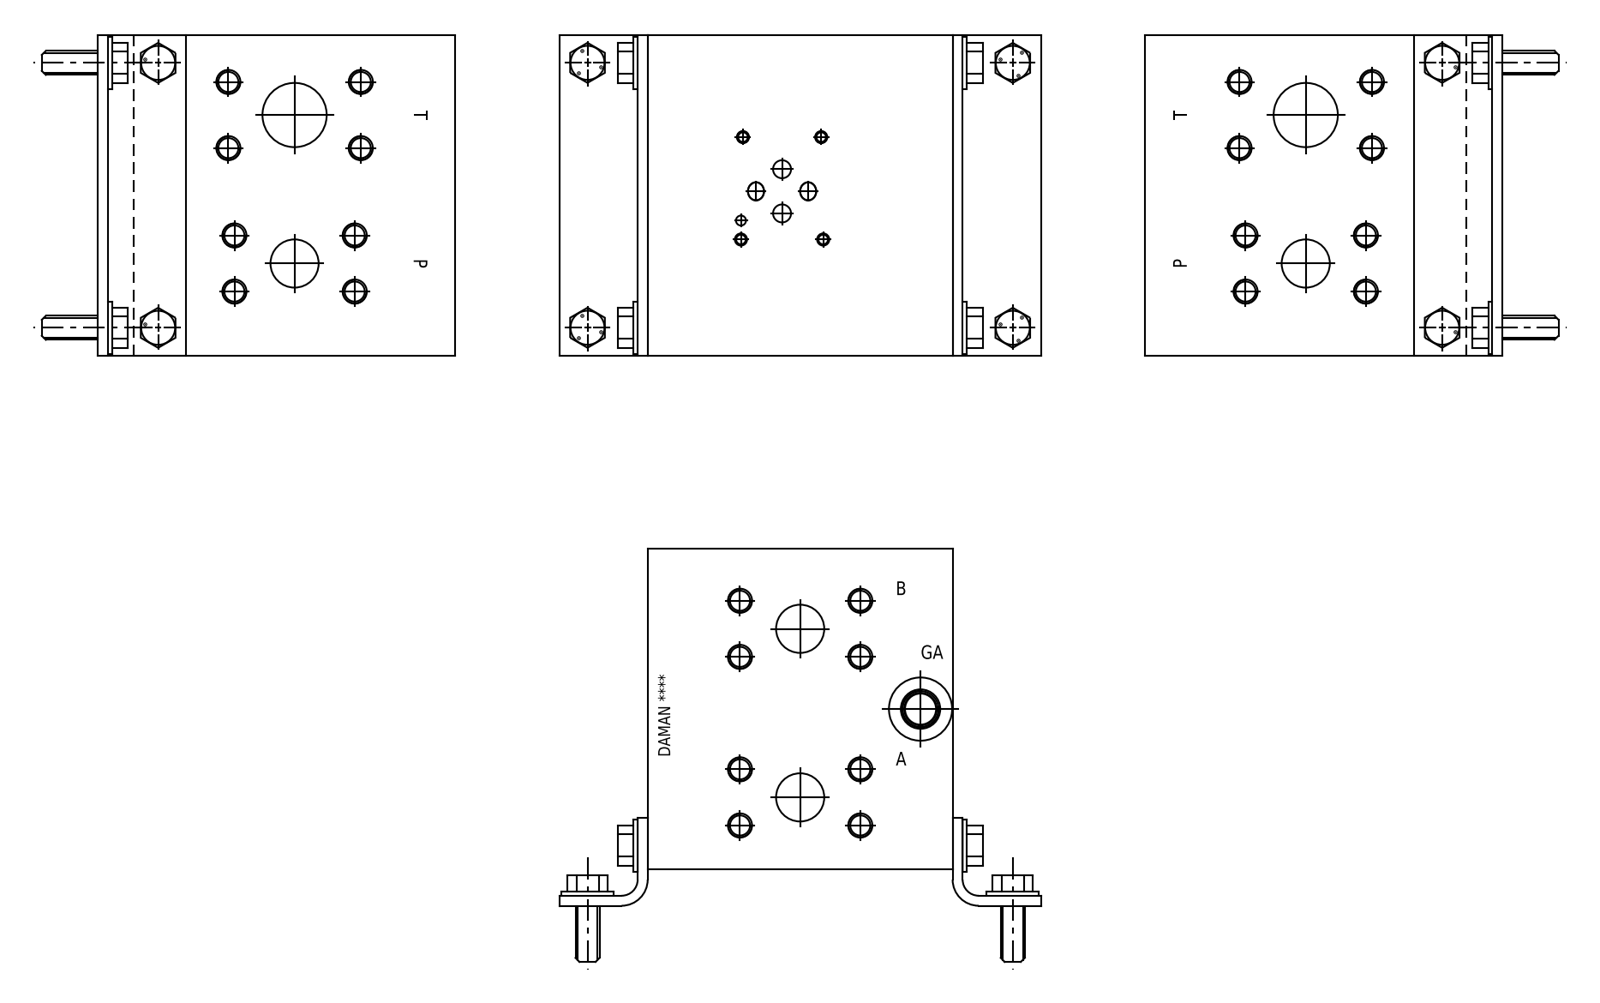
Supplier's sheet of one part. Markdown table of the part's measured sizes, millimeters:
| quantity | value |
| --- | --- |
| part name | Part_AD03HP014F_3D |
| STEP written by | Autodesk Inventor 2020 (AUTOMOTIVE_DESIGN) |
| units | millimeters |
| bodies | 1 solid, 600 faces (361 planar, 80 cylindrical, 159 other) |
| overall size | 127 × 127 × 120.65 |
| volume | 1 871 000 mm³ |
| surface area | 120 351 mm² |
| round holes (diameter × count) | 7.92 × 18, 9.53 × 18, 4.22 × 4, 5 × 4, 7.14 × 4, 19.05 × 3, 3.96 × 1, 12.29 × 1, 12.9 × 1, 14.27 × 1, 14.53 × 1, 25.02 × 1 |
| main face-to-face distances | 127, 120.65, 22.1, 98.55, 0.79, 126.21, 22.06, 21.31, 104.9, 76.45 |
| hole center spacings | 26.26, 22.19, 26.25, 29.27, 47.59, 52.51, 60.46, 66.68 |
